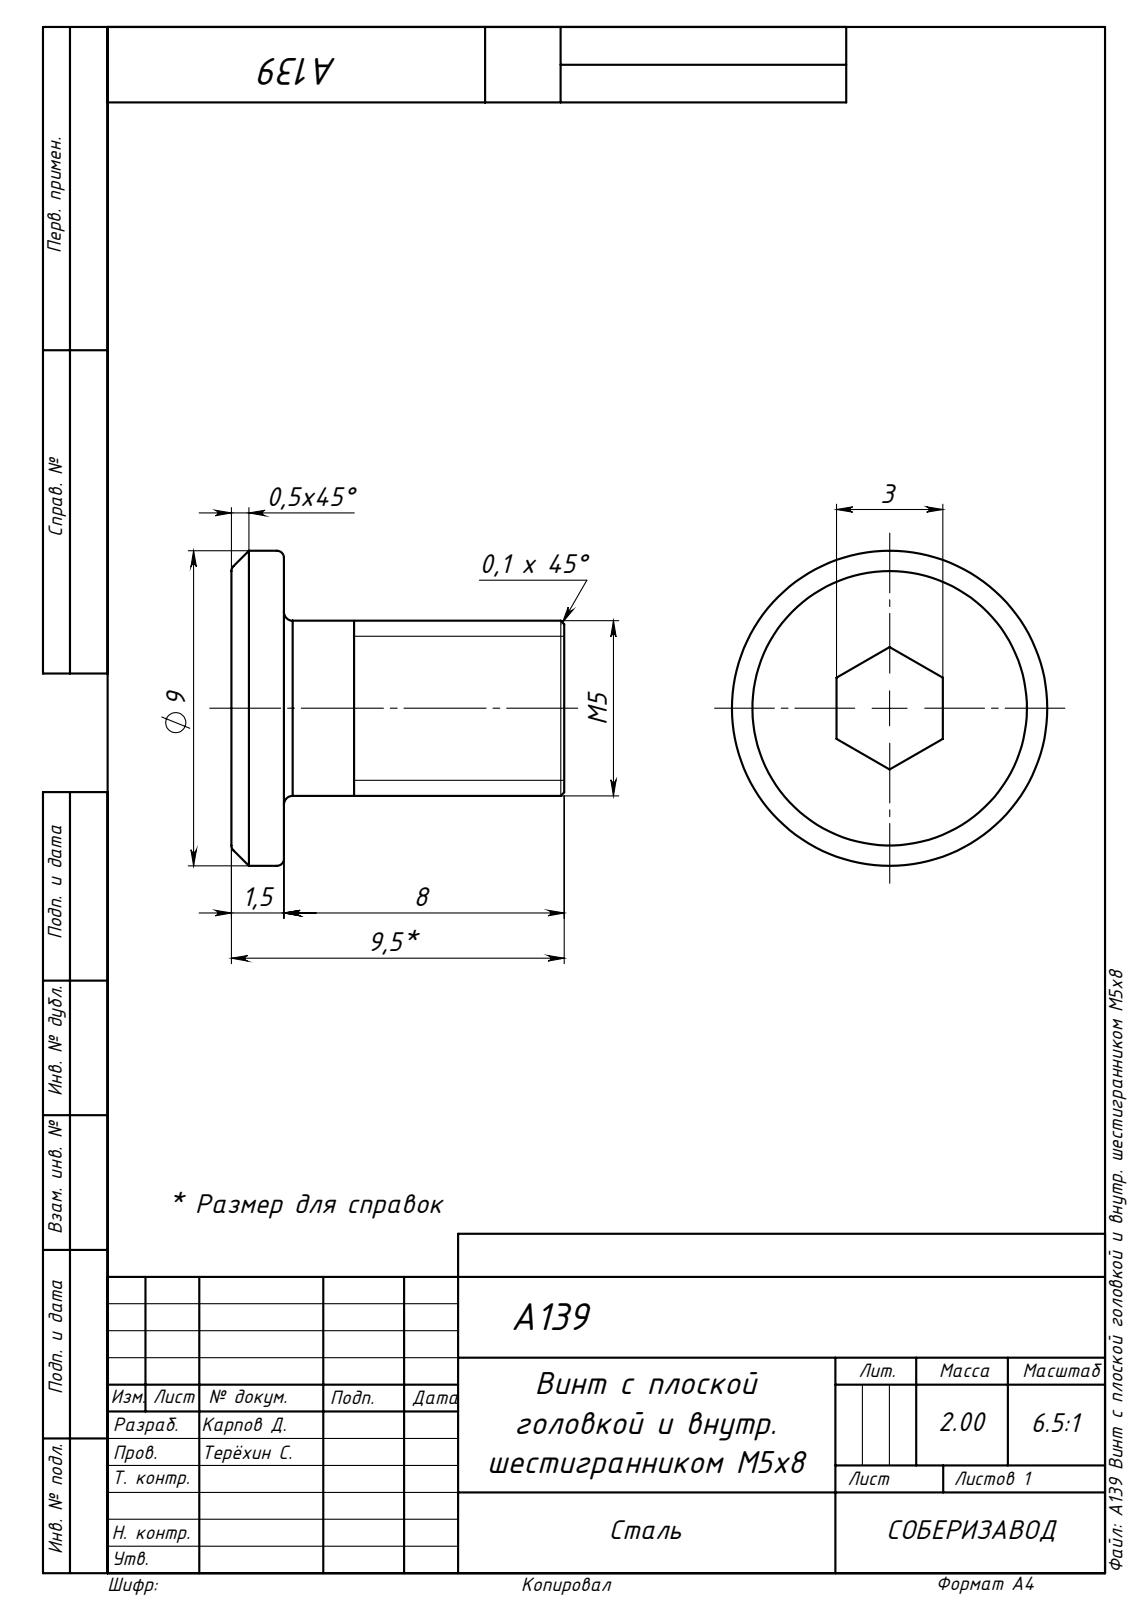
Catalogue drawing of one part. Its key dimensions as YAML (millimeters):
step_written_by: "SolidWorks 2020 (AUTOMOTIVE_DESIGN)"
units: millimeters
bodies: {solids: 1, faces: 24, planar: 10, cylindrical: 4, other: 10}
overall_size: [9.5, 9, 9]
volume: 237
surface_area: 297
round_bosses_or_shafts:
  - {diameter: 9, count: 1}
  - {diameter: 5, count: 1}
face_to_face_distances: [1.5, 8, 9.5, 3.04]
